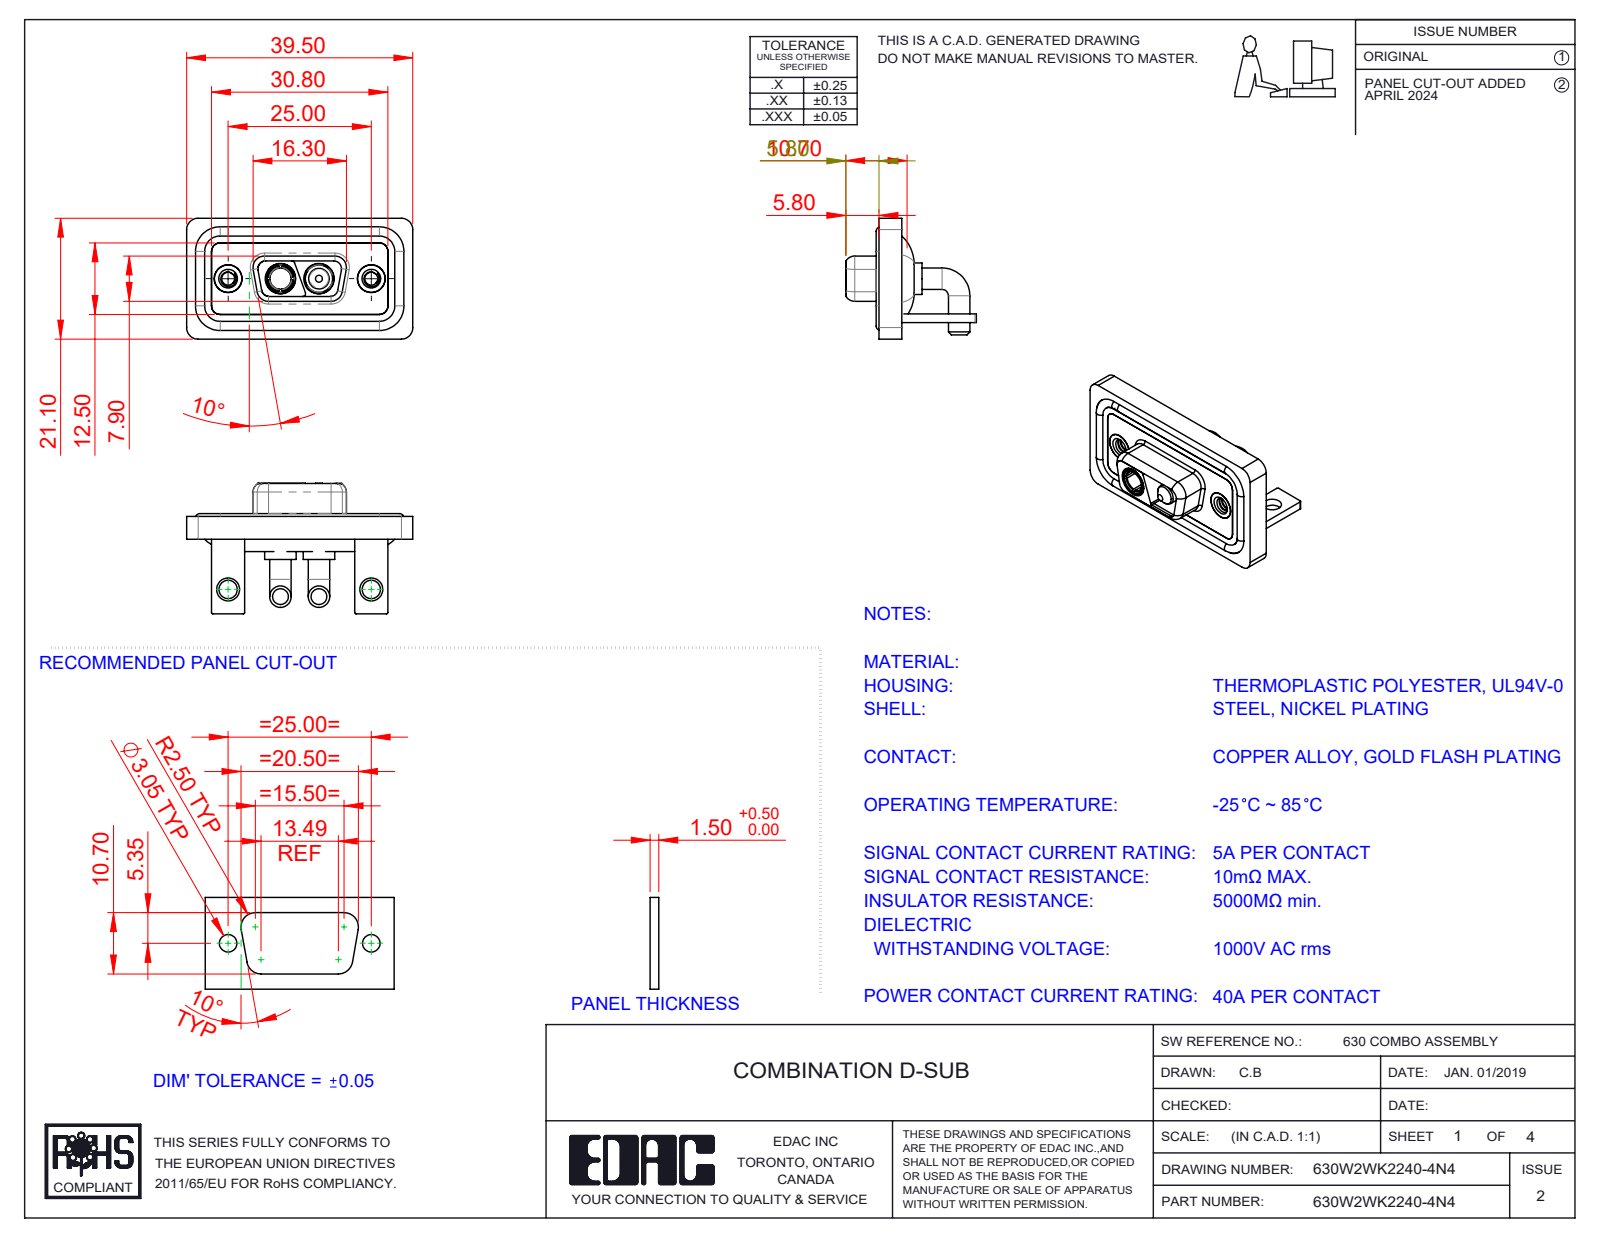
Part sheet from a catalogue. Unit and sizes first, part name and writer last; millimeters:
Units: millimetres
Overall size (bounding box): 39.5 × 22.8 × 21.1
Round holes (diameter × count): ⌀4.85 ×4, ⌀2.26 ×2, ⌀3.2 ×2, ⌀4 ×2, ⌀4.05 ×2, ⌀5 ×2, ⌀5.3 ×2, ⌀3.7 ×1
Round bosses / shafts (diameter × count): ⌀3.75 ×4, ⌀1.6 ×4, ⌀5.5 ×2, ⌀5.2 ×2, ⌀4.95 ×2, ⌀4.8 ×2, ⌀4.75 ×2, ⌀4.96 ×1
Partial cylindrical surfaces — rounded edges, fillets, slot ends (radius × count): R2 ×19, R1.5 ×18, R0.25 ×16, R1.35 ×8, R1.6 ×8, R0.5 ×7, R0.6 ×4, R0.65 ×4
Main face-to-face distances: 0.4, 2.9, 1.5, 1.1, 3.7, 1.8, 0.8, 2.5, 1.6, 3.1
Hole centre spacings: 9.14, 15.86, 25, 6.72
Volume: 5 219 mm³ · Surface area: 8 317 mm²
Bodies: 13 solids, 556 faces (164 planar, 259 cylindrical, 133 other)
Part name (STEP PRODUCT): 630Combo Housing_2WK2; 630Combo Shell Front_09 Contacts; 630Combo Threaded Rivet_2; Power Pin_40A RA (+5 more)
STEP written by: SolidWorks 2023 (CONFIG_CONTROL_DESIGN)
